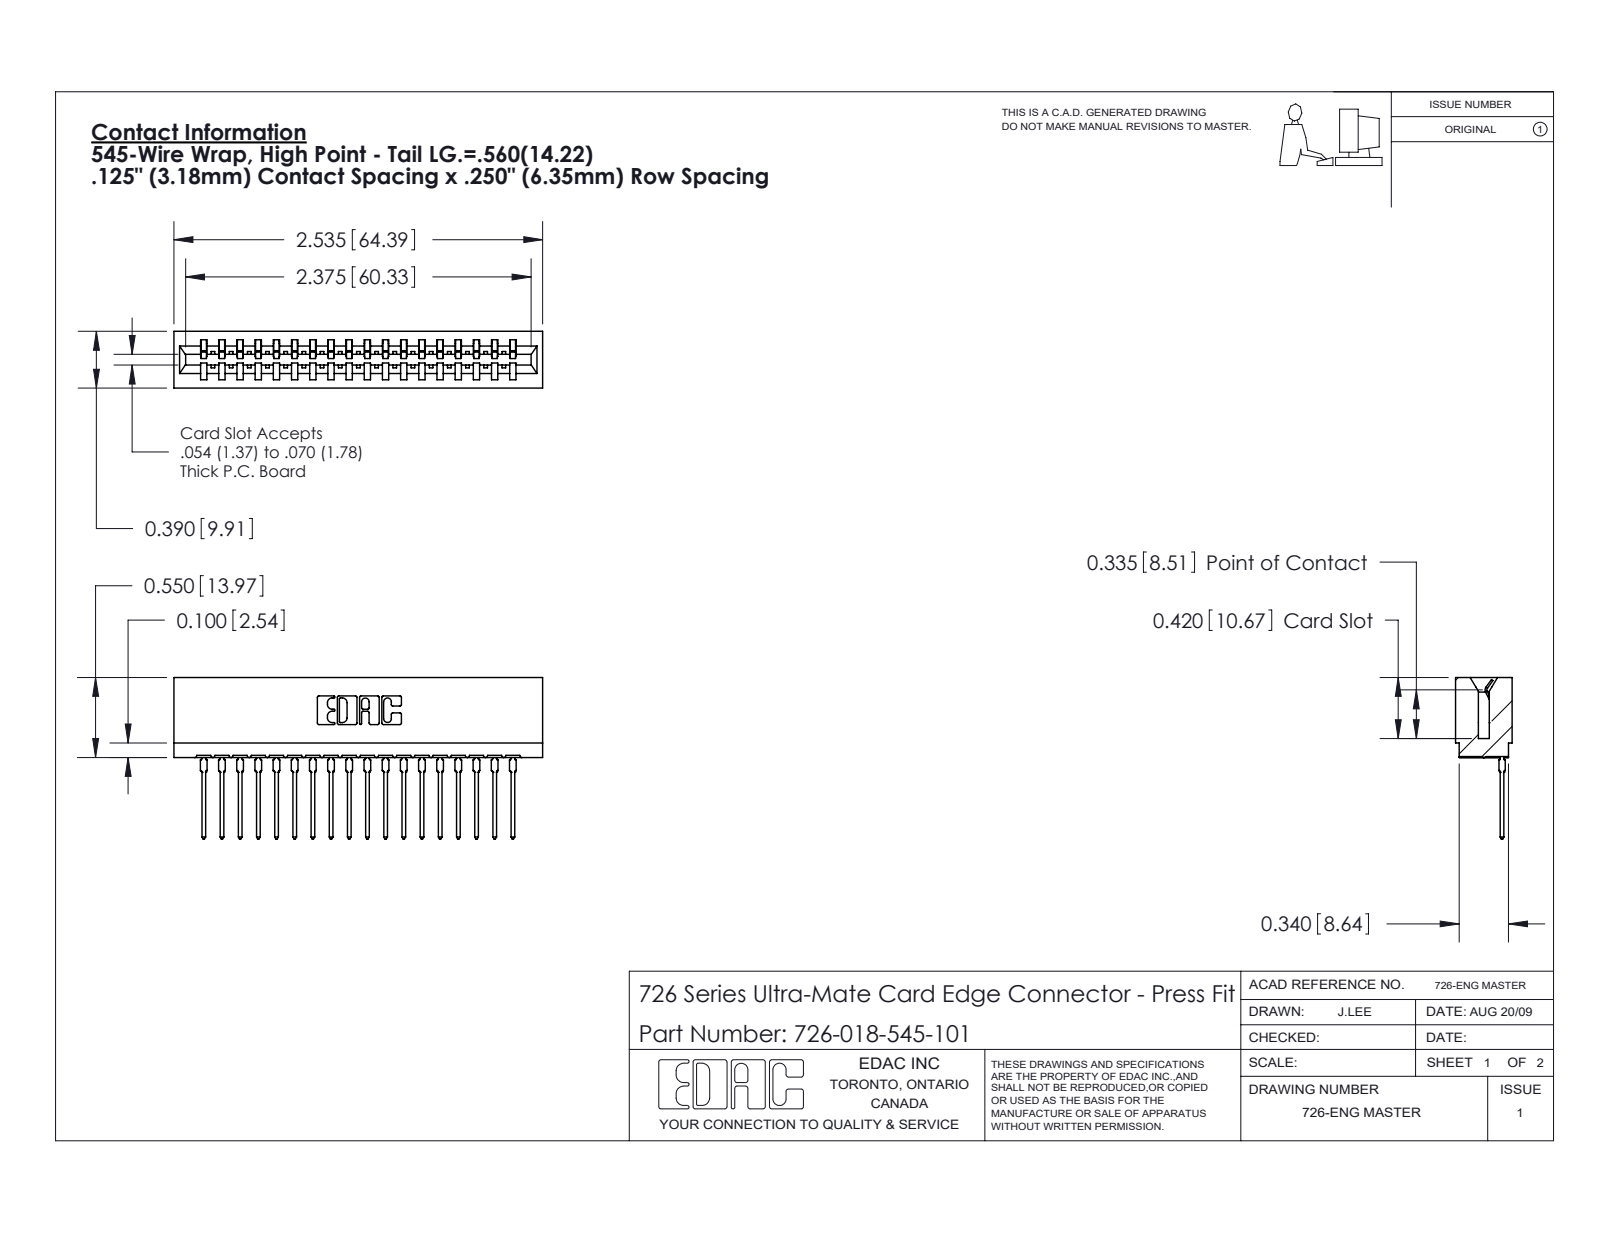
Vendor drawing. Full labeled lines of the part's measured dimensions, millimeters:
Part name (STEP PRODUCT): 726 Part_.515 Slot Depth - 01; 726-018-545-101; 746-292-001_545
STEP written by: SolidWorks 2020 (CONFIG_CONTROL_DESIGN)
Units: millimetres
Bodies: 19 solids, 2041 faces (1189 planar, 384 cylindrical, 468 other)
Overall size (bounding box): 64.4 × 28.2 × 9.9
Volume: 5 930 mm³ · Surface area: 8 961 mm²
Partial cylindrical surfaces — rounded edges, fillets, slot ends (radius × count): R0.5 ×36, R0.3 ×22, R0.4 ×19, R0.2 ×6, R0.8 ×6, R0.1 ×4, R0.3 ×4, R0.7 ×3
Main face-to-face distances: 1.4, 8.5, 9.9, 6.4, 0.6, 7.8, 2.1, 19.1, 12.7, 3.2
